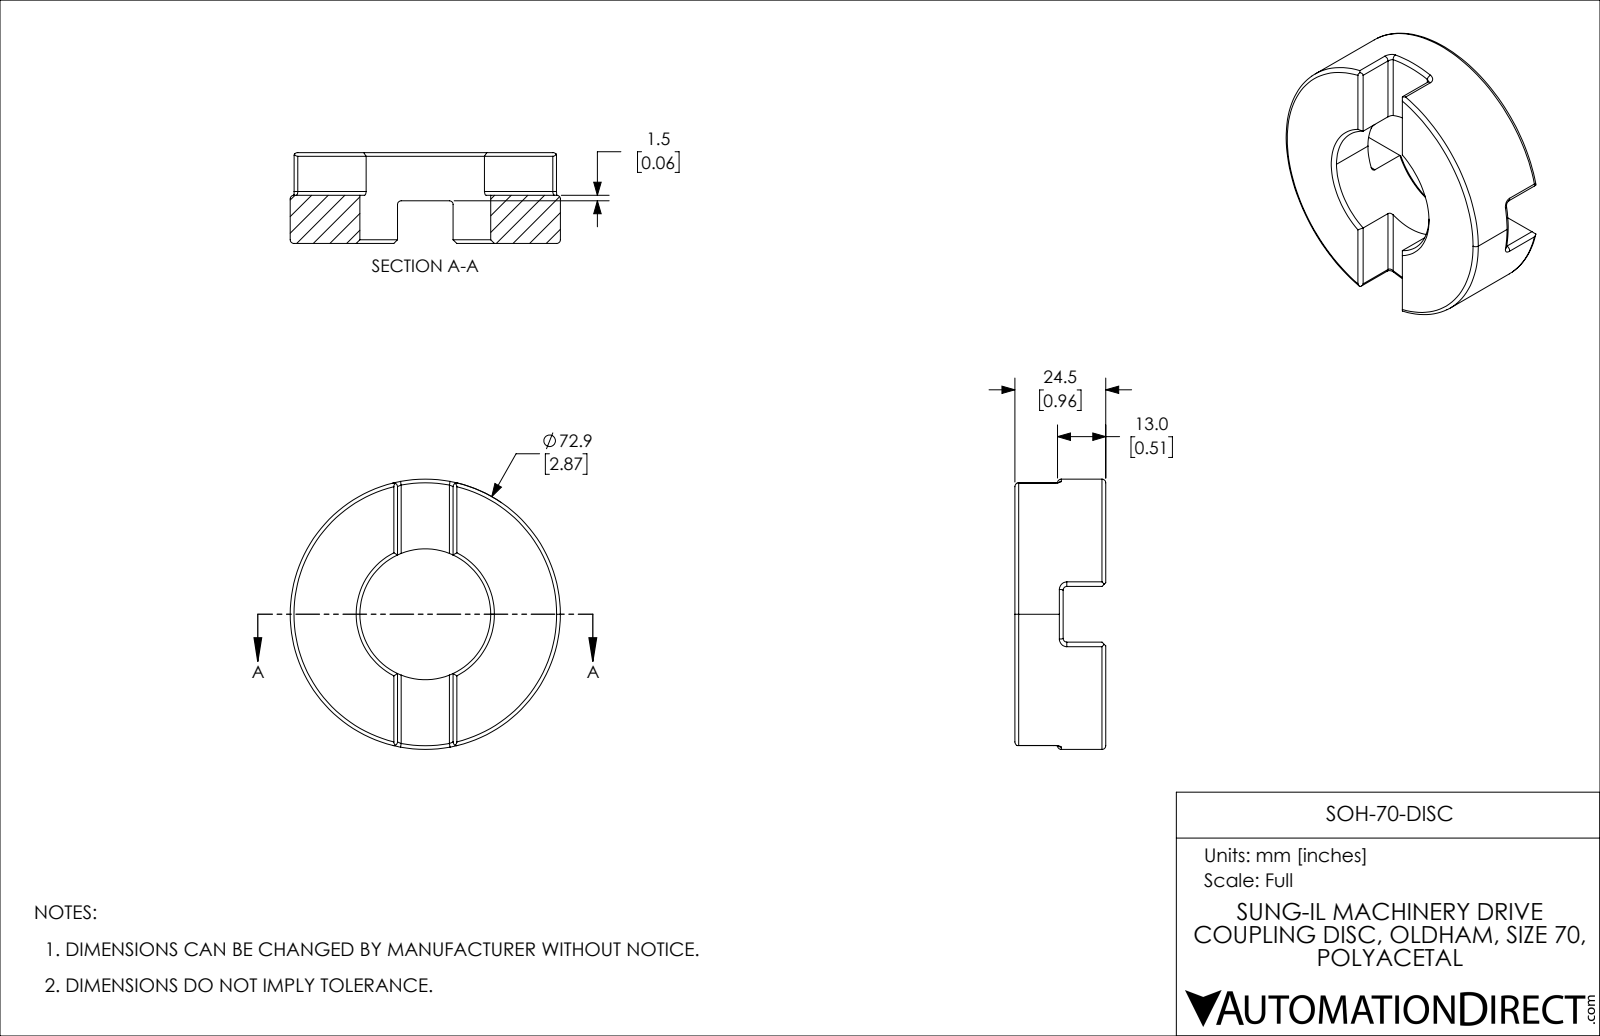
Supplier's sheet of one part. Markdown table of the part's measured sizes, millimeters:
| quantity | value |
| --- | --- |
| part name | SOH-70-DISC |
| STEP written by | SolidWorks 2021 (CONFIG_CONTROL_DESIGN) |
| units | millimeters |
| bodies | 1 solid, 69 faces (24 planar, 22 cylindrical, 23 other) |
| overall size | 72.9 × 72.9 × 24.5 |
| volume | 64 861 mm³ |
| surface area | 14 612 mm² |
| round holes (diameter × count) | 35.3 × 1 |
| round bosses / shafts (diameter × count) | 72.9 × 1 |
| partial cylindrical surfaces (radius × count) | 1 × 12 |
| main face-to-face distances | 24.5, 11.5, 13, 15, 1.5 |
